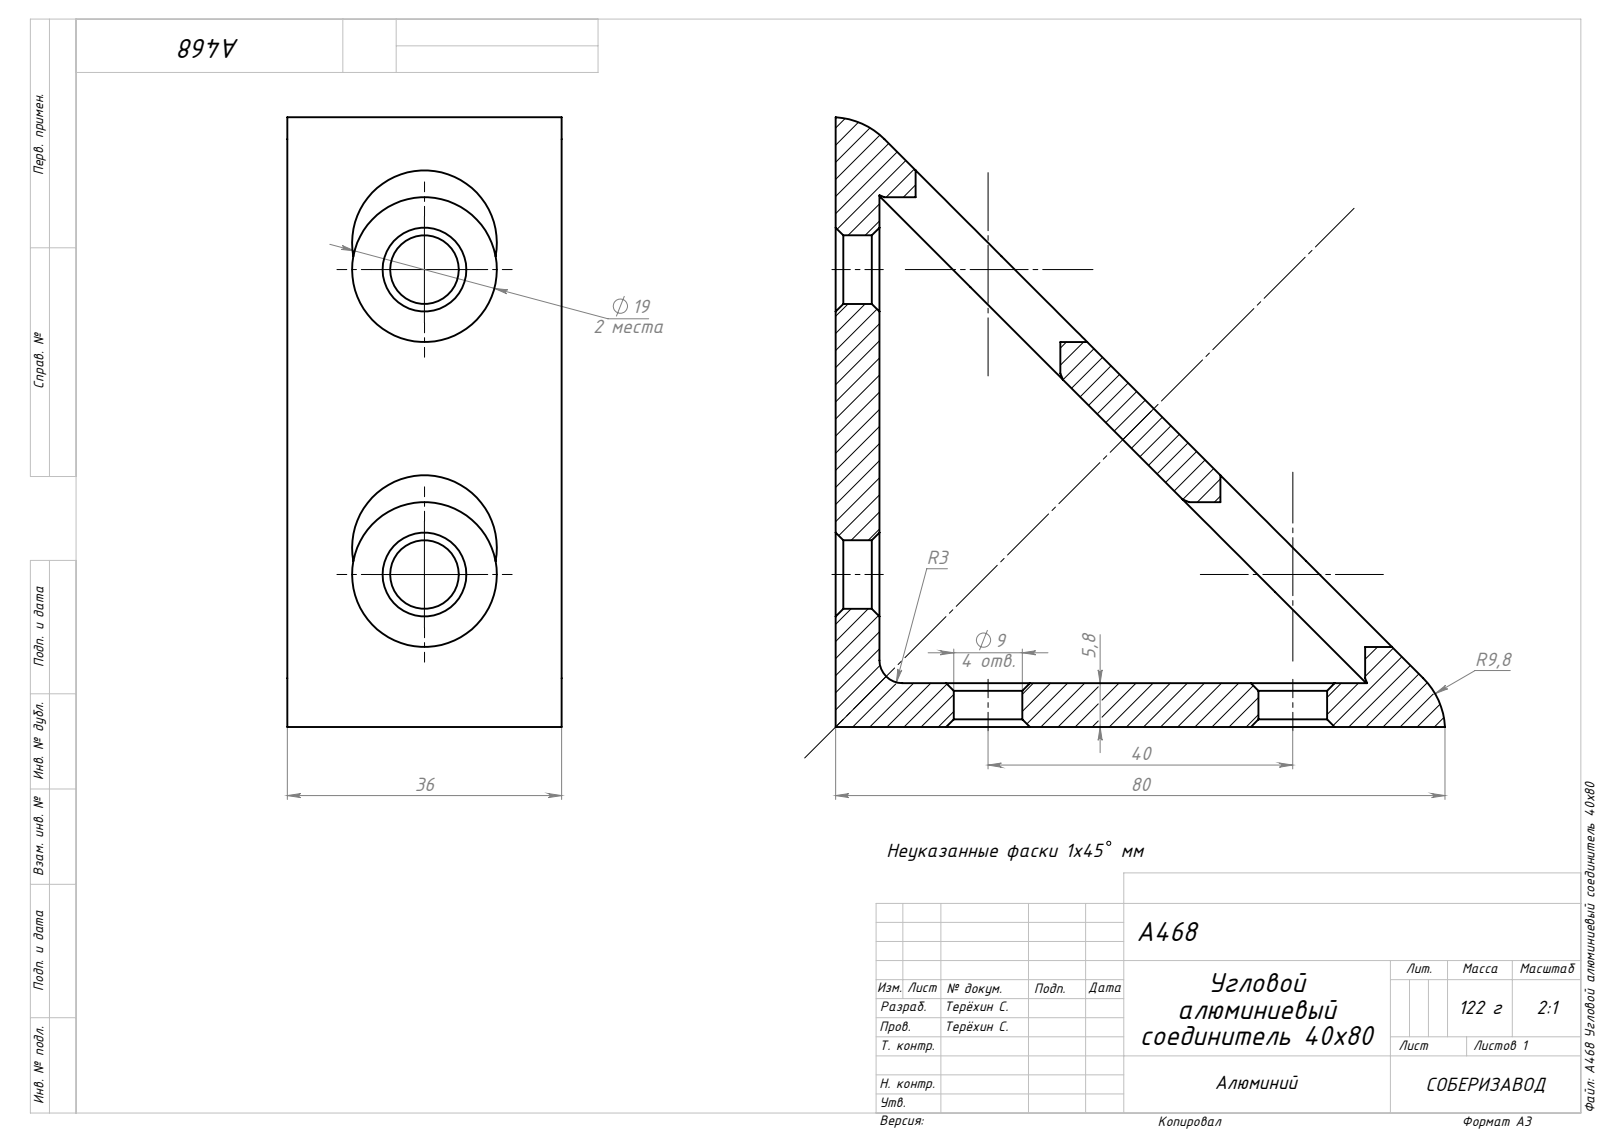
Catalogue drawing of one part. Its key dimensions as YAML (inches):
part_name: "A468 Угловой алюминиевый соединитель 40х80"
step_written_by: "SolidWorks 2021 (AUTOMOTIVE_DESIGN)"
units: inches
bodies: {solids: 1, faces: 51, planar: 8, cylindrical: 23, other: 20}
overall_size: [3.149, 3.149, 1.417]
volume: 2.727
surface_area: 30.25
round_holes:
  - {diameter: 0.354, count: 4}
  - {diameter: 0.748, count: 4}
partial_cylinders:
  - {radius: 0.387, count: 2}
  - {radius: 0.118, count: 1}
face_to_face_distances: [0.226, 1.417]
hole_center_spacings: [1.575]
